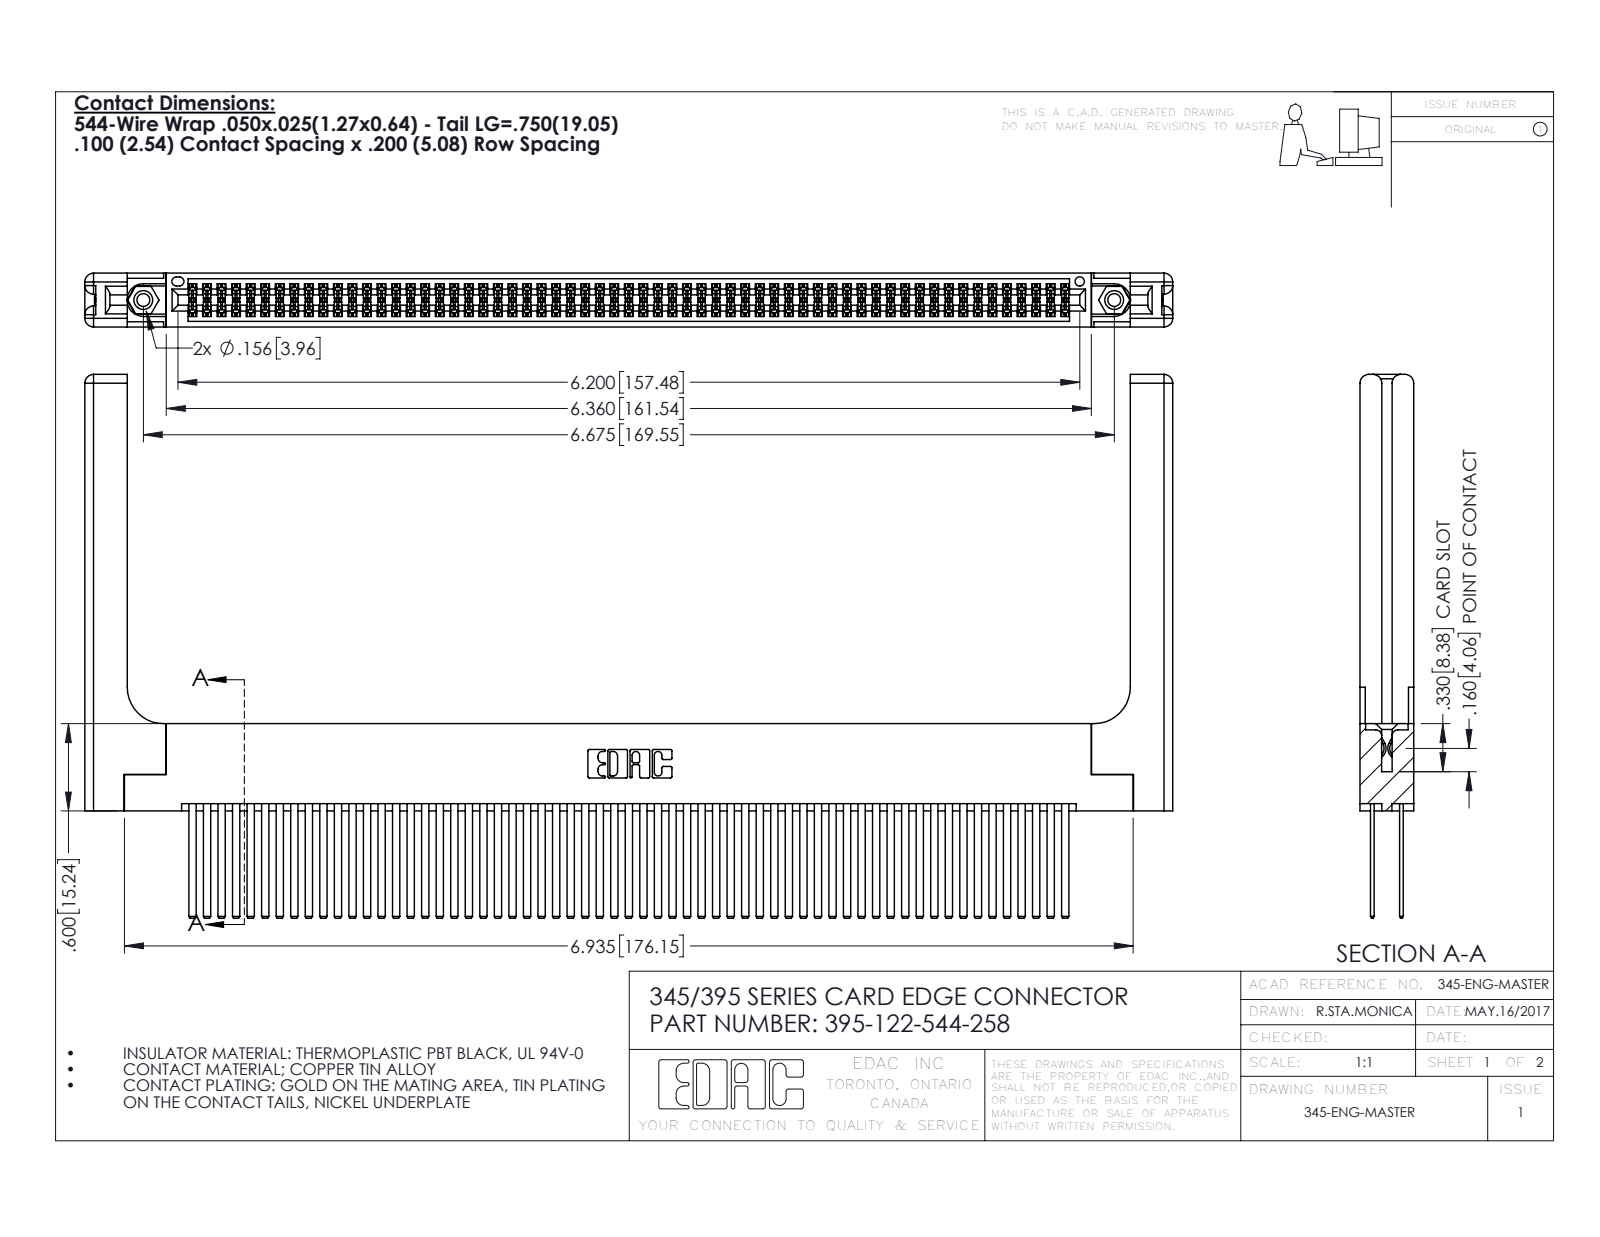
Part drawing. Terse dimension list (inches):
name: 345 Part_Flush Mounting Lugs - 0.156 Dia-TH; 345-292-001_345-293-144; 395-122-544-258; 345-220-058_345-220-058 (+1 more)
written by: SolidWorks 2016 (CONFIG_CONTROL_DESIGN)
unit: in
bodies: 127 solids, 5750 faces (3766 planar, 1924 cylindrical, 60 other)
size: 7.479 × 3.737 × 0.37
volume: 1.758 in³; area: 62.78 in²
holes: 2× ⌀0.089, 2× ⌀0.125, 2× ⌀0.156, 1× ⌀0.064
bosses: 2× ⌀0.155
rounds: 183× R0.006, 22× R0.01, 16× R0.06, 6× R0.007, 6× R0.031, 3× R0.026, 2× R0.014, 2× R0.019
face distances: 0.072, 0.298, 0.2, 0.098, 0.272, 0.025, 0.225, 0.37, 0.175, 0.148
hole spacings: 0.27, 6.439, 6.675
